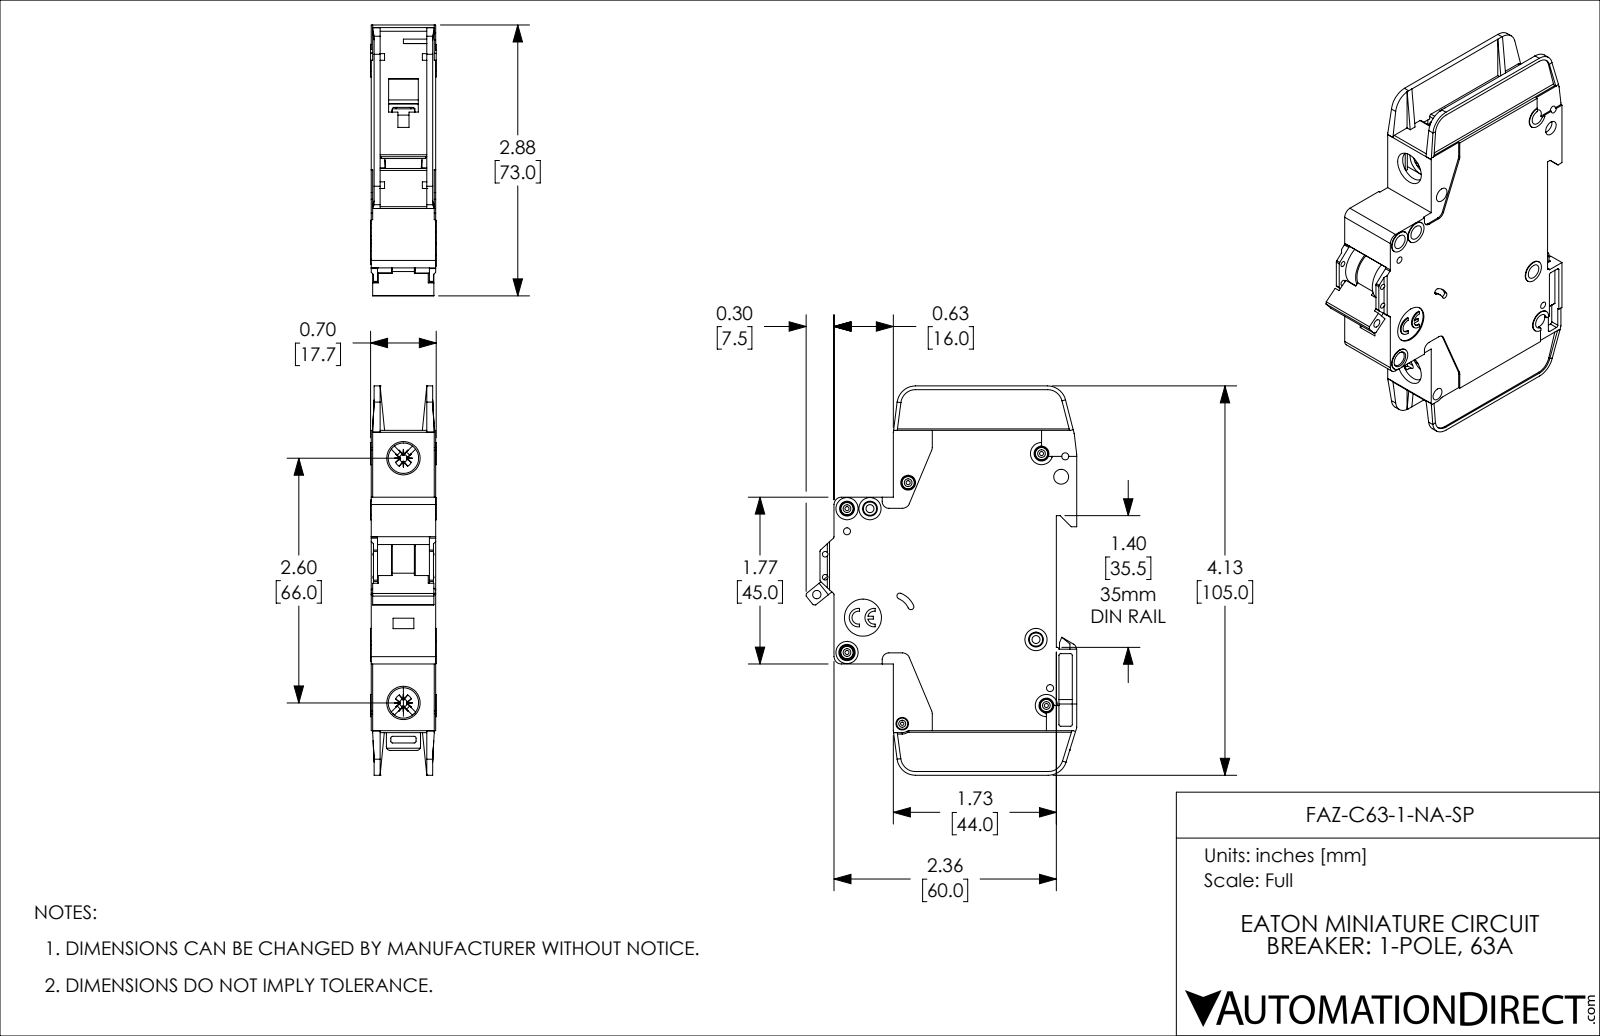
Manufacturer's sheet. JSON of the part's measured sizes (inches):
{"part_name": "FAZ-C63-1-NA-SP", "step_written_by": "SolidWorks 2019 (AUTOMOTIVE_DESIGN)", "units": "inches", "bodies": {"solids": 1, "faces": 1127, "planar": 671, "cylindrical": 357, "other": 99}, "overall_size": [4.134, 2.876, 0.697], "volume_in3": 4.682, "surface_area_in2": 41.01, "round_holes": [[0.157, 8], [0.043, 5], [0.075, 4], [0.059, 2], [0.085, 2], [0.323, 2], [0.035, 1], [0.089, 1], [0.098, 1], [0.134, 1], [0.394, 1]], "round_bosses_or_shafts": [[0.13, 5], [0.236, 4], [0.118, 2], [0.098, 1]], "partial_cylinders_radius": [[0.02, 42], [0.016, 10], [0.039, 10], [0.079, 8], [0.197, 5], [0.008, 4], [0.026, 4], [0.043, 4]], "face_to_face_distances": [0.047, 0.685, 0.591, 0.638, 0.094, 0.543, 0.016, 0.031, 0.496, 0.575], "hole_center_spacings": [0.244, 0.537, 0.87, 0.189, 0.199, 0.204, 0.221, 0.24]}
